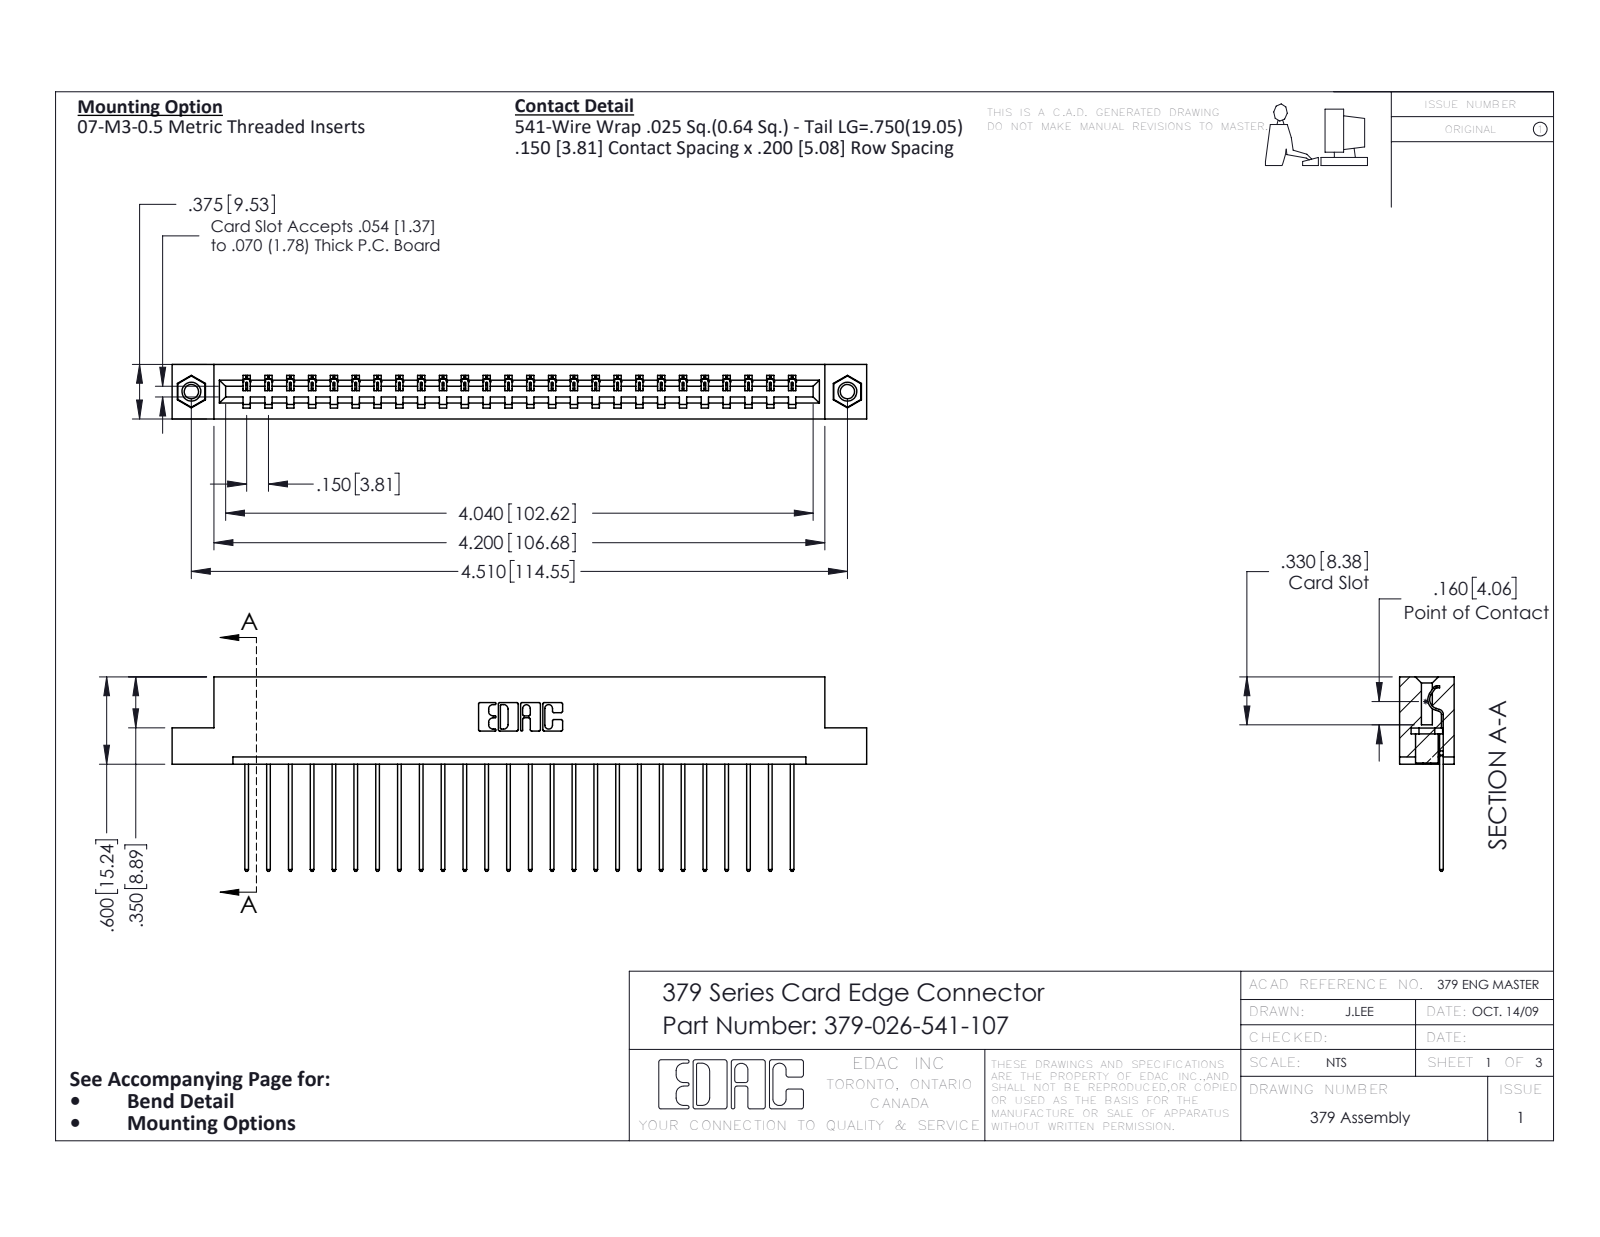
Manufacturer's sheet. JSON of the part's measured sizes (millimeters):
{"part_name": "345-250-001_345-250-005-103; 379-026-541-107; 379 Part_Flush - .156 Dia - TI; 345-292-001_345-293-141", "step_written_by": "SolidWorks 2016 (CONFIG_CONTROL_DESIGN)", "units": "millimeters", "bodies": {"solids": 29, "faces": 1682, "planar": 1194, "cylindrical": 472, "other": 16}, "overall_size": [121.3, 34, 9.5], "volume_mm3": 12600, "surface_area_mm2": 13410, "round_holes": [[2.5, 2], [3.2, 2], [4, 2]], "round_bosses_or_shafts": [[3.9, 2]], "partial_cylinders_radius": [[0.2, 52], [0.3, 52], [0.3, 22], [0.2, 6], [0.8, 6], [0.7, 3], [0.4, 1], [0.6, 1]], "face_to_face_distances": [7.6, 1.9, 9.5, 5.7, 15.2, 7, 2.5, 0.6, 5.1, 3.8], "hole_center_spacings": [114.6]}
